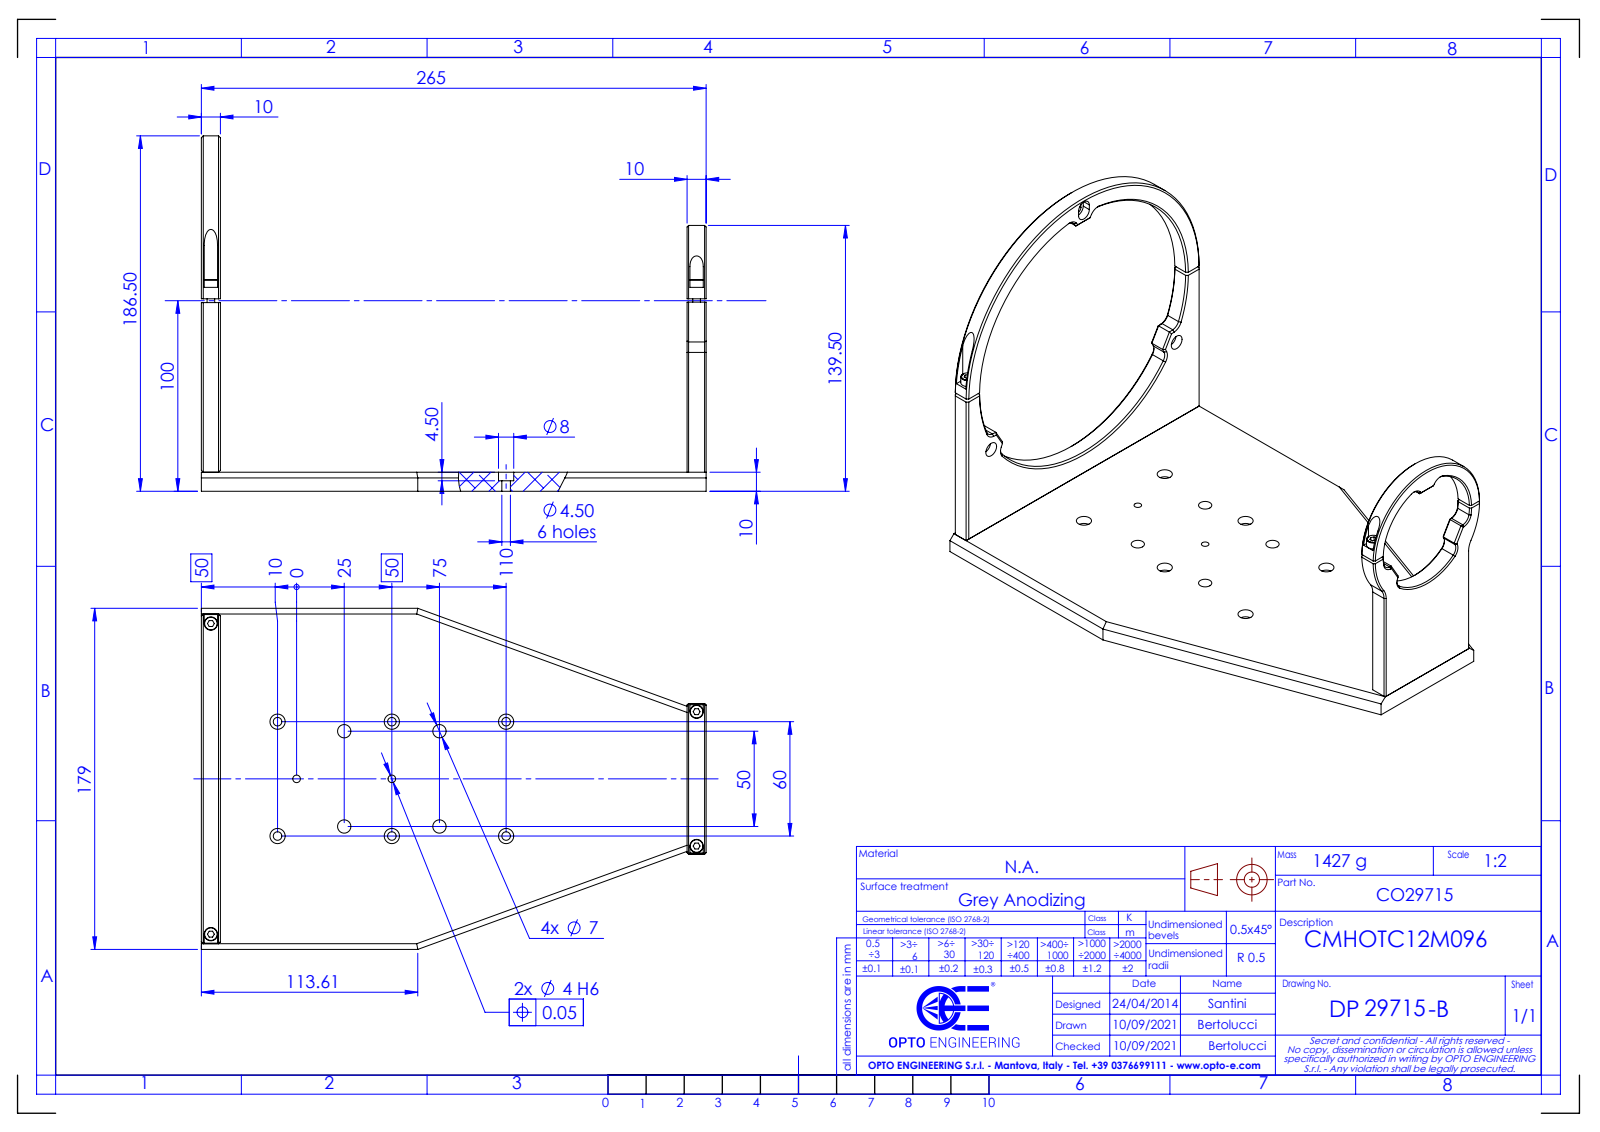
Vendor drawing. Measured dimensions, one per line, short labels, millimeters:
name: DP29715-B_CMHOTC12M096
written by: SolidWorks 2021 (CONFIG_CONTROL_DESIGN)
unit: mm
bodies: 0 solids, 342 faces (162 planar, 104 cylindrical, 76 other)
size: 265 × 186.5 × 179
holes: 12× ⌀8, 8× ⌀4.5, 6× ⌀7, 2× ⌀4, 1× ⌀153
bosses: 2× ⌀7, 2× ⌀4
rounds: 12× R5, 2× R2.25, 2× R4, 2× R10, 1× R32, 1× R39.5, 1× R86.5
face distances: 10, 255, 265, 245, 3, 176, 58.1, 120.9, 55.1, 117.9
hole spacings: 35.36, 60, 50, 25.5, 60.42, 65.19, 67.08, 84.85
